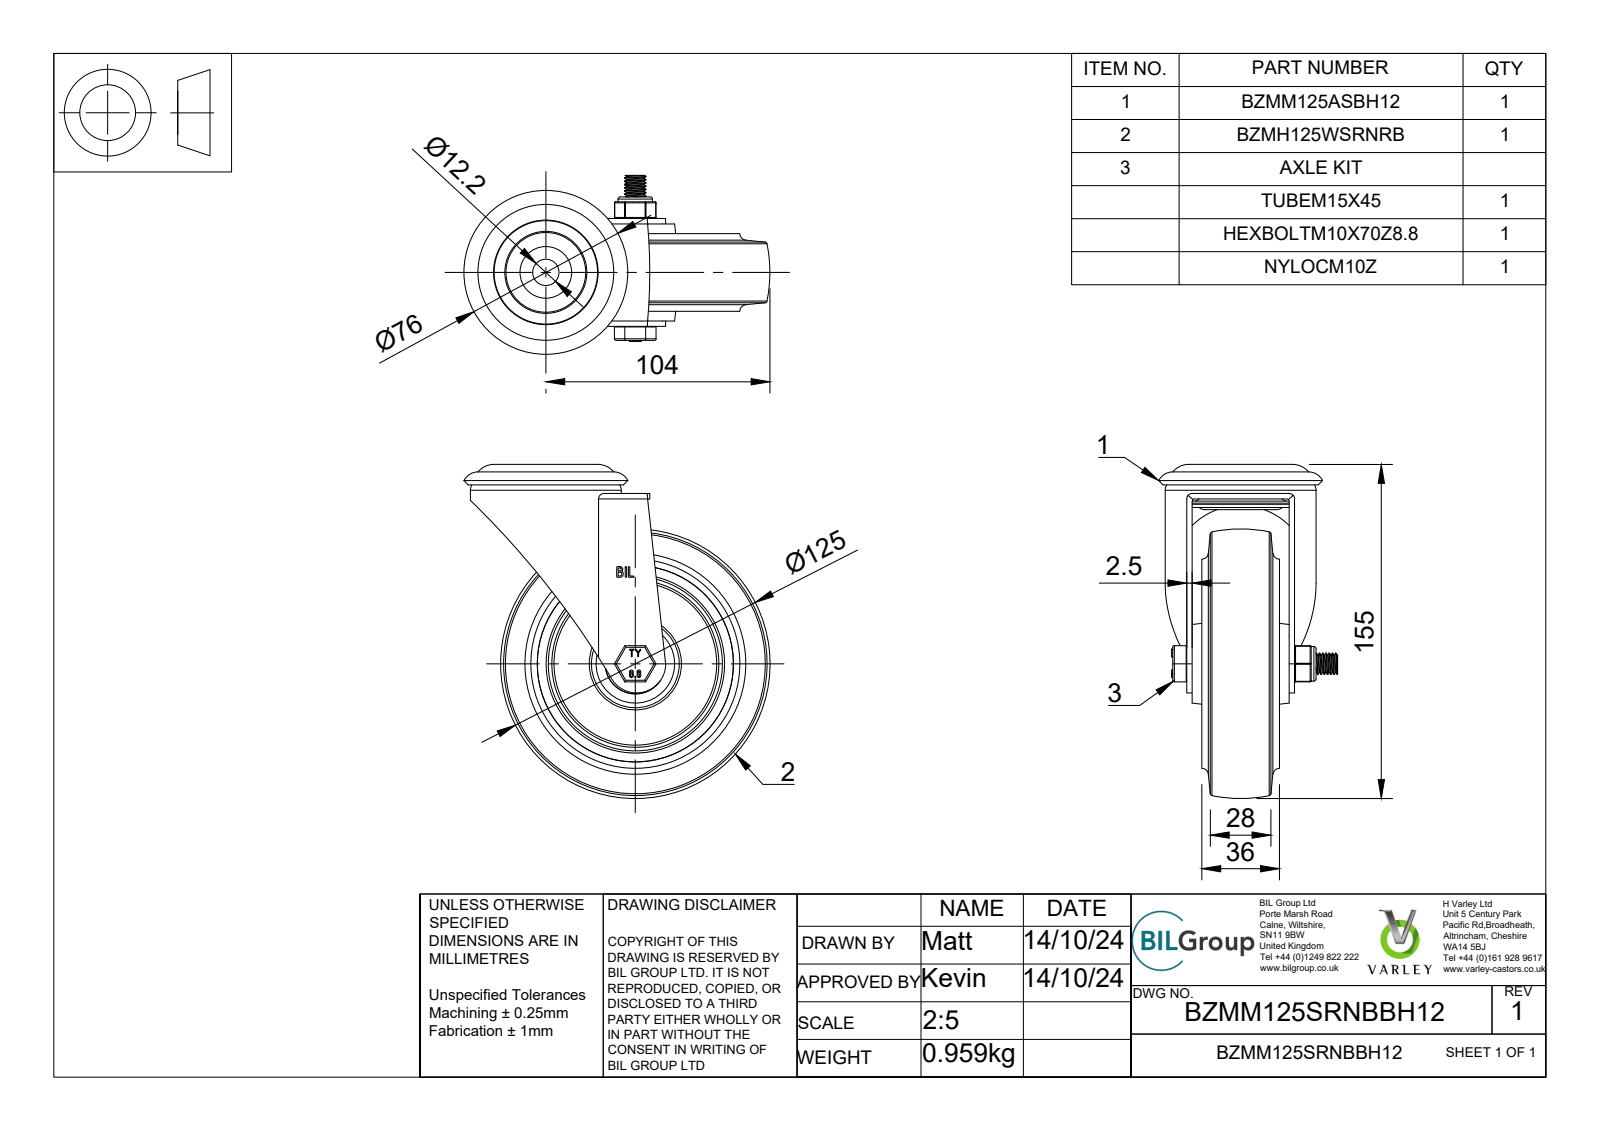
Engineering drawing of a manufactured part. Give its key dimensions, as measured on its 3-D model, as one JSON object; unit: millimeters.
{"part_name": "BZMM125SRNBBH12 v3; BZMM125ASBH12 v1; ZINC PLATED, PRESSED STEEL HEAD; ZINC PLATED, PRESSED STEEL FORKS (+8 more)", "step_written_by": "Autodesk Translation Framework v13.20.0.188 (AUTOMOTIVE_DESIGN)", "units": "millimeters", "bodies": {"solids": 19, "faces": 434, "planar": 195, "cylindrical": 132, "other": 107}, "overall_size": [155, 142, 83], "volume_mm3": 359142, "surface_area_mm2": 135312, "round_holes": [[10, 1], [10.2, 1], [12, 1], [12.2, 1], [15.2, 1], [15.5, 1], [17, 1], [23.5, 1], [28, 1], [65, 1], [72, 1], [91, 1]], "round_bosses_or_shafts": [[3.4, 9], [70, 1], [49.5, 1], [38, 1], [27.9, 1], [24, 1], [22, 1], [21.31, 1]], "partial_cylinders_radius": [[0.5, 18], [0.75, 6], [1.25, 4], [2.5, 2], [9.5, 1], [13.5, 1], [253.62, 1], [408.21, 1]], "face_to_face_distances": [2.5, 20, 25, 22.5, 47.5, 27.5, 7, 4.5, 43, 40.5]}
